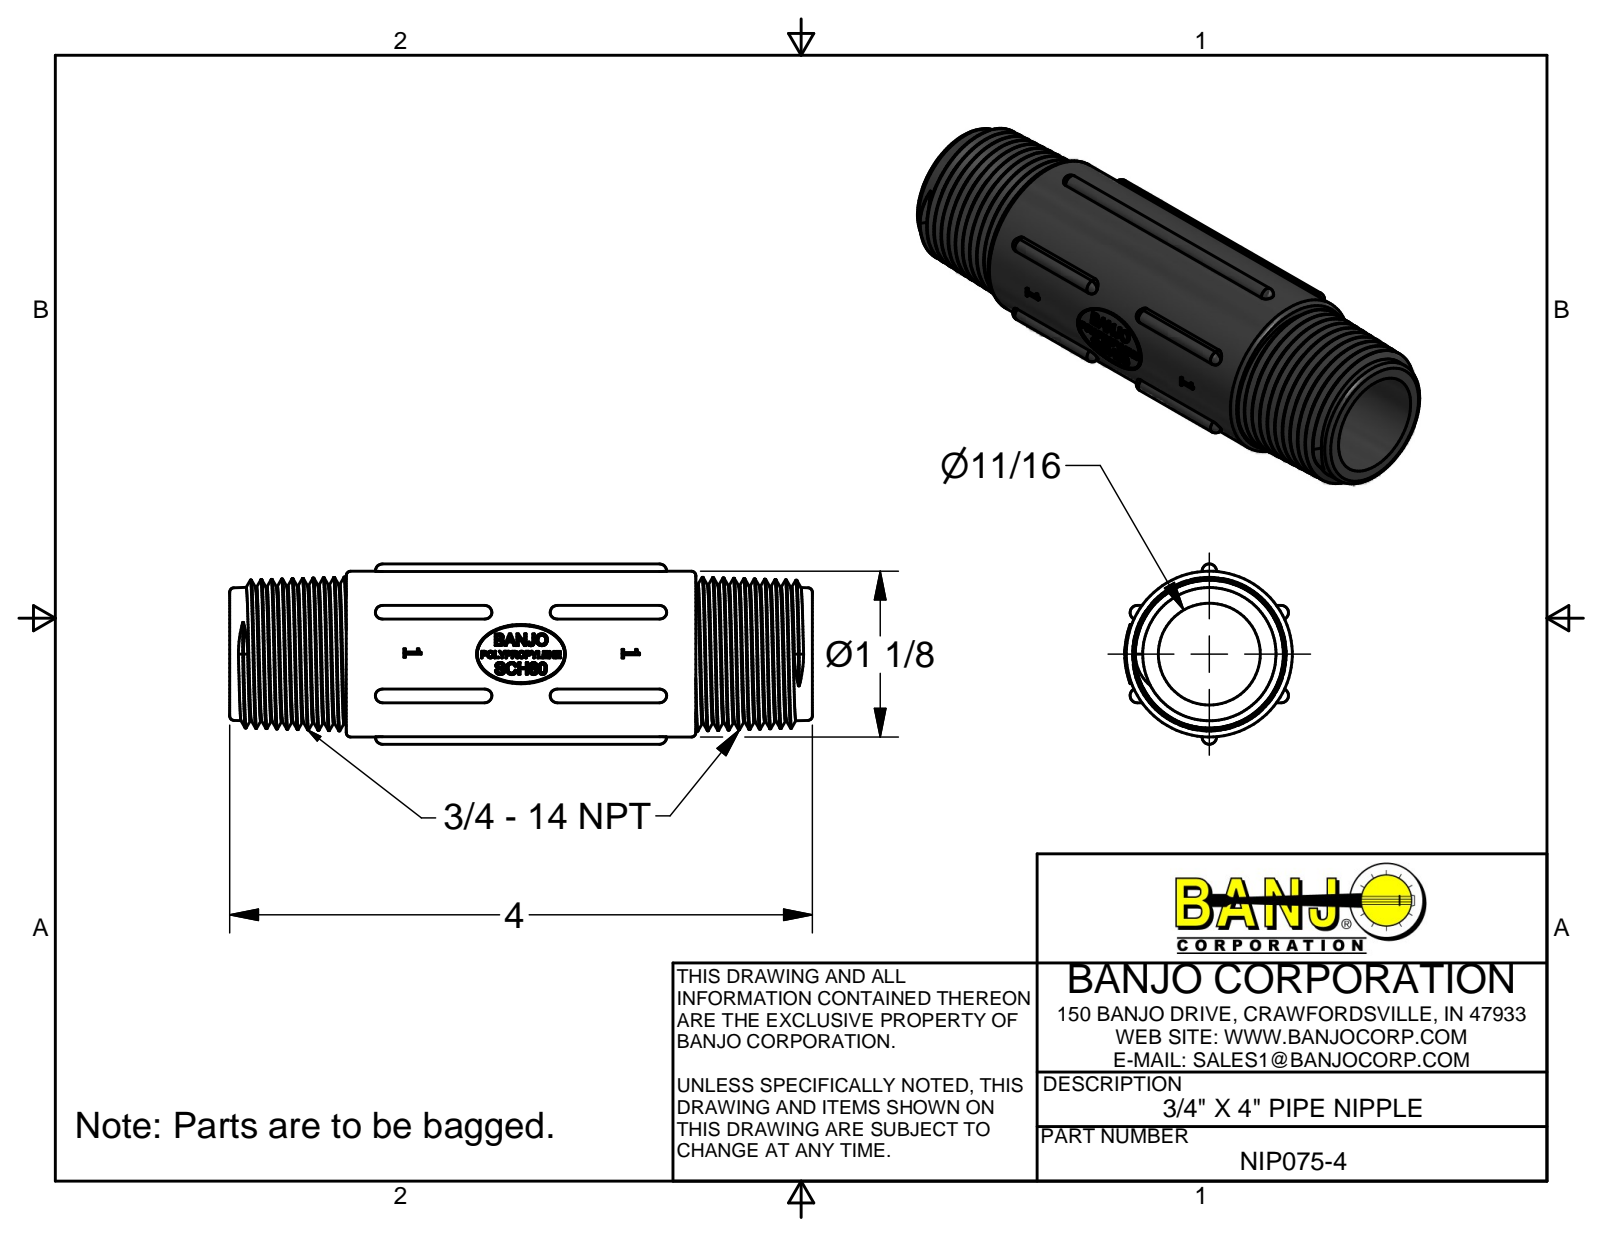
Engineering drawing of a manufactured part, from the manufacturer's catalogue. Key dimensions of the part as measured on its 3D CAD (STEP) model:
Part name (STEP PRODUCT): NIP075-4
STEP written by: Autodesk Inventor 2014 (AUTOMOTIVE_DESIGN)
Units: millimetres
Bodies: 1 solid, 417 faces (56 planar, 64 cylindrical, 297 other)
Overall size (bounding box): 101.6 × 31.5 × 29.21
Volume: 35 326 mm³ · Surface area: 17 708 mm²
Round holes (diameter × count): ⌀17.78 ×1
Round bosses / shafts (diameter × count): ⌀28.96 ×1
Partial cylindrical surfaces — rounded edges, fillets, slot ends (radius × count): R1.27 ×14, R7.09 ×1, R14.73 ×1
Main face-to-face distances: 20.32, 81.28, 101.6, 60.96, 17.02, 38.05, 0.31, 30.36, 10.04, 50.92
